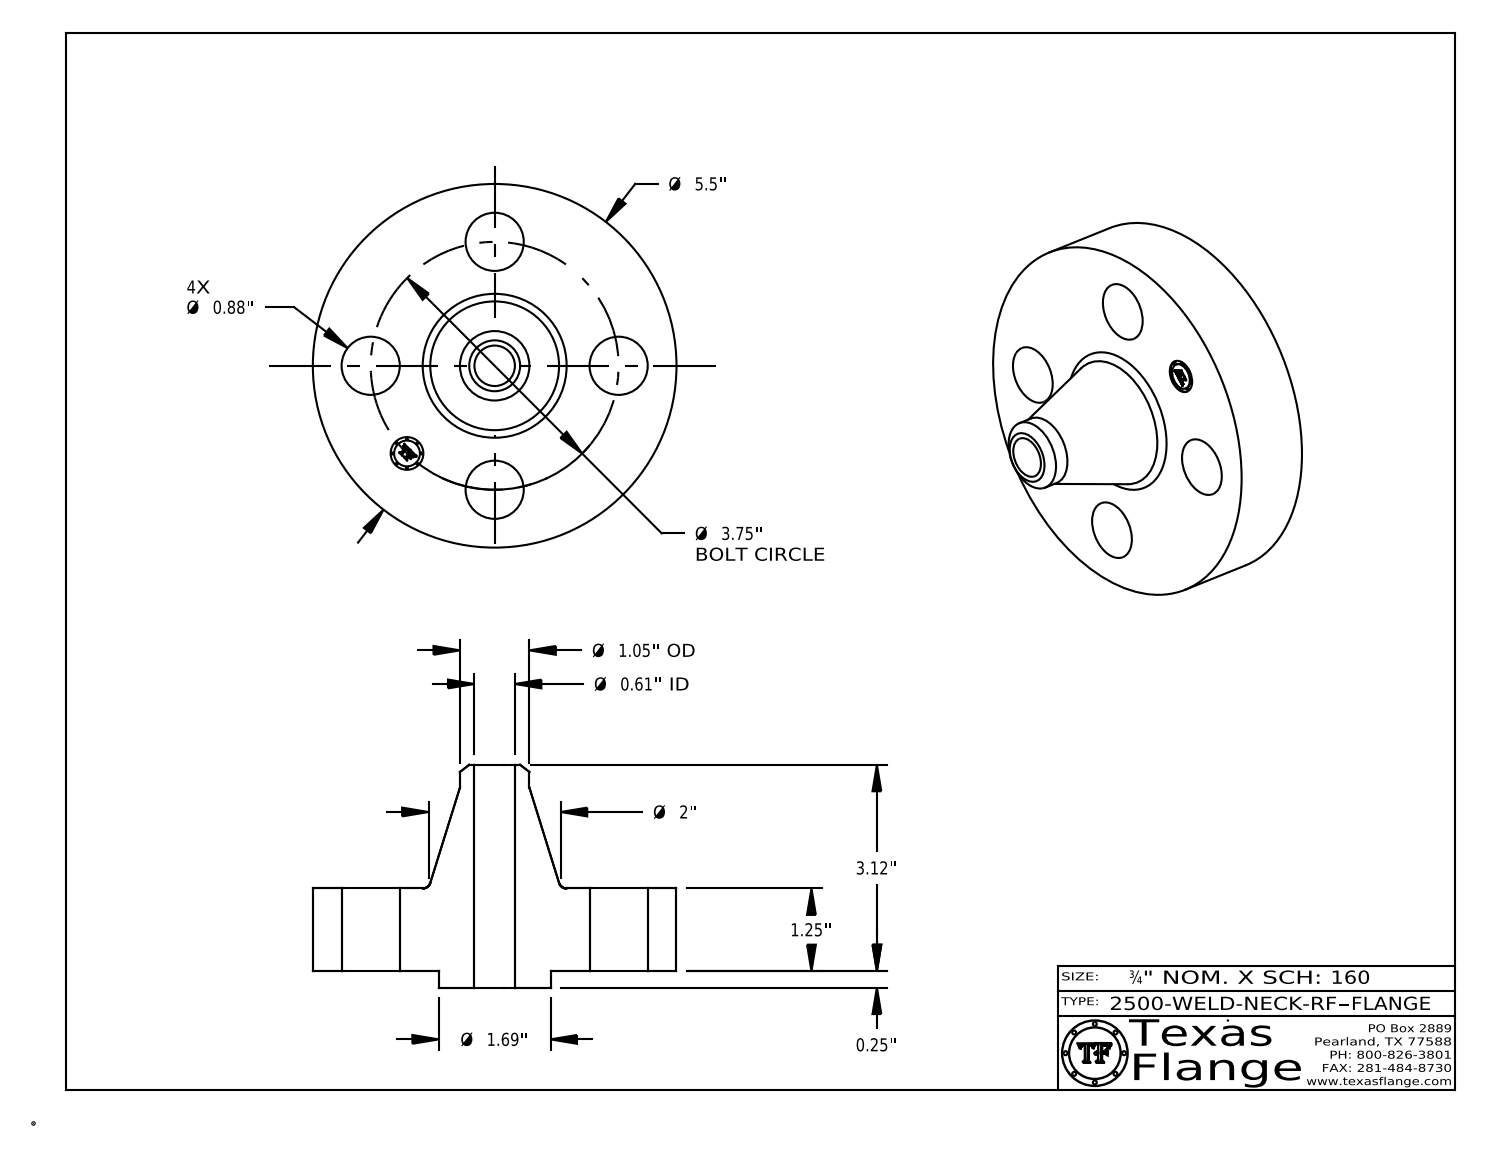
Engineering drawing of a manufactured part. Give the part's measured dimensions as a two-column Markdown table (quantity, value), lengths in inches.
| quantity | value |
| --- | --- |
| part name | 2500-WELD-NECK-RF |
| STEP written by | CATIA V5 STEP AP214 (AUTOMOTIVE_DESIGN) |
| units | inches |
| bodies | 1 solid, 411 faces (369 planar, 36 cylindrical, 6 other) |
| overall size | 5.5 × 5.5 × 3.37 |
| volume | 29.39 in³ |
| surface area | 91.5 in² |
| round holes (diameter × count) | 0.88 × 4, 0.495 × 1, 0.612 × 1 |
| round bosses / shafts (diameter × count) | 0.03 × 8, 5.5 × 1, 1.69 × 1, 1.05 × 1, 0.39 × 1 |
| main face-to-face distances | 1.25, 0.25, 1.5, 3.37, 3.12, 1.87, 1.485, 1.235, 0.015, 1.885 |
| hole center spacings | 1.875, 2.652, 1.435, 3.465, 3.75 |
